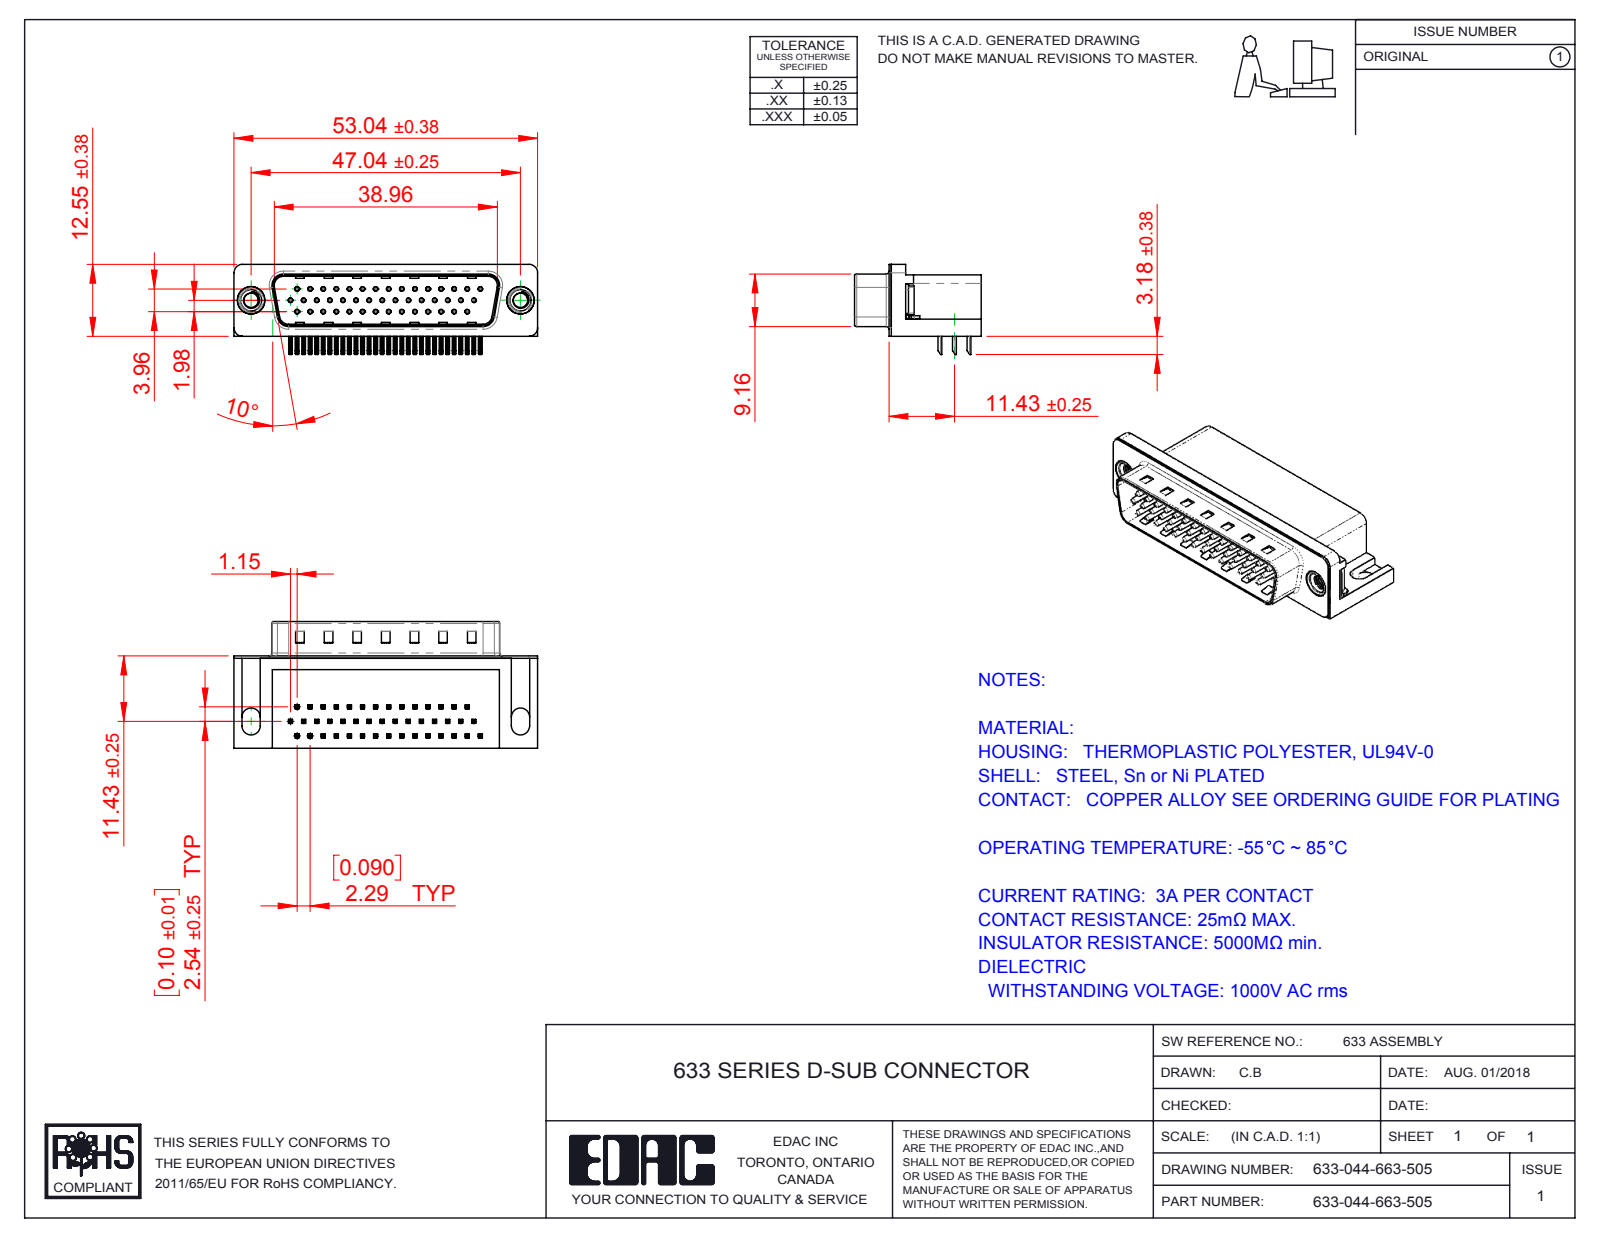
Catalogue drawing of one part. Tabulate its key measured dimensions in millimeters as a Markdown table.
| quantity | value |
| --- | --- |
| part name | 633 Housing_44 Contact; 633 M3 Threaded Rivet; 633 Shell_44 Contact; 633 Contact Bottom (+4 more) |
| STEP written by | SolidWorks 2016 (CONFIG_CONTROL_DESIGN) |
| units | millimeters |
| bodies | 50 solids, 3686 faces (2317 planar, 1060 cylindrical, 309 other) |
| overall size | 53.04 × 22.1 × 15.73 |
| volume | 8 062 mm³ |
| surface area | 9 999 mm² |
| round holes (diameter × count) | 0.35 × 44, 0.8 × 44, 2.5 × 2, 4 × 2, 4.8 × 2, 5 × 2 |
| round bosses / shafts (diameter × count) | 0.75 × 44, 4.9 × 2, 4.75 × 2, 3.9 × 2 |
| partial cylindrical surfaces (radius × count) | 0.25 × 184, 0.12 × 88, 1 × 16, 0.5 × 9, 1.6 × 8, 1.5 × 7, 0.9 × 4, 2 × 4 |
| main face-to-face distances | 0.4, 10.35, 15.7, 8.76, 2.9, 2.5, 2.1, 16.1, 10.7, 2.54 |
| hole center spacings | 2.29, 4.57, 4.58, 2.28, 6.87, 9.16, 11.45, 2.27 |
